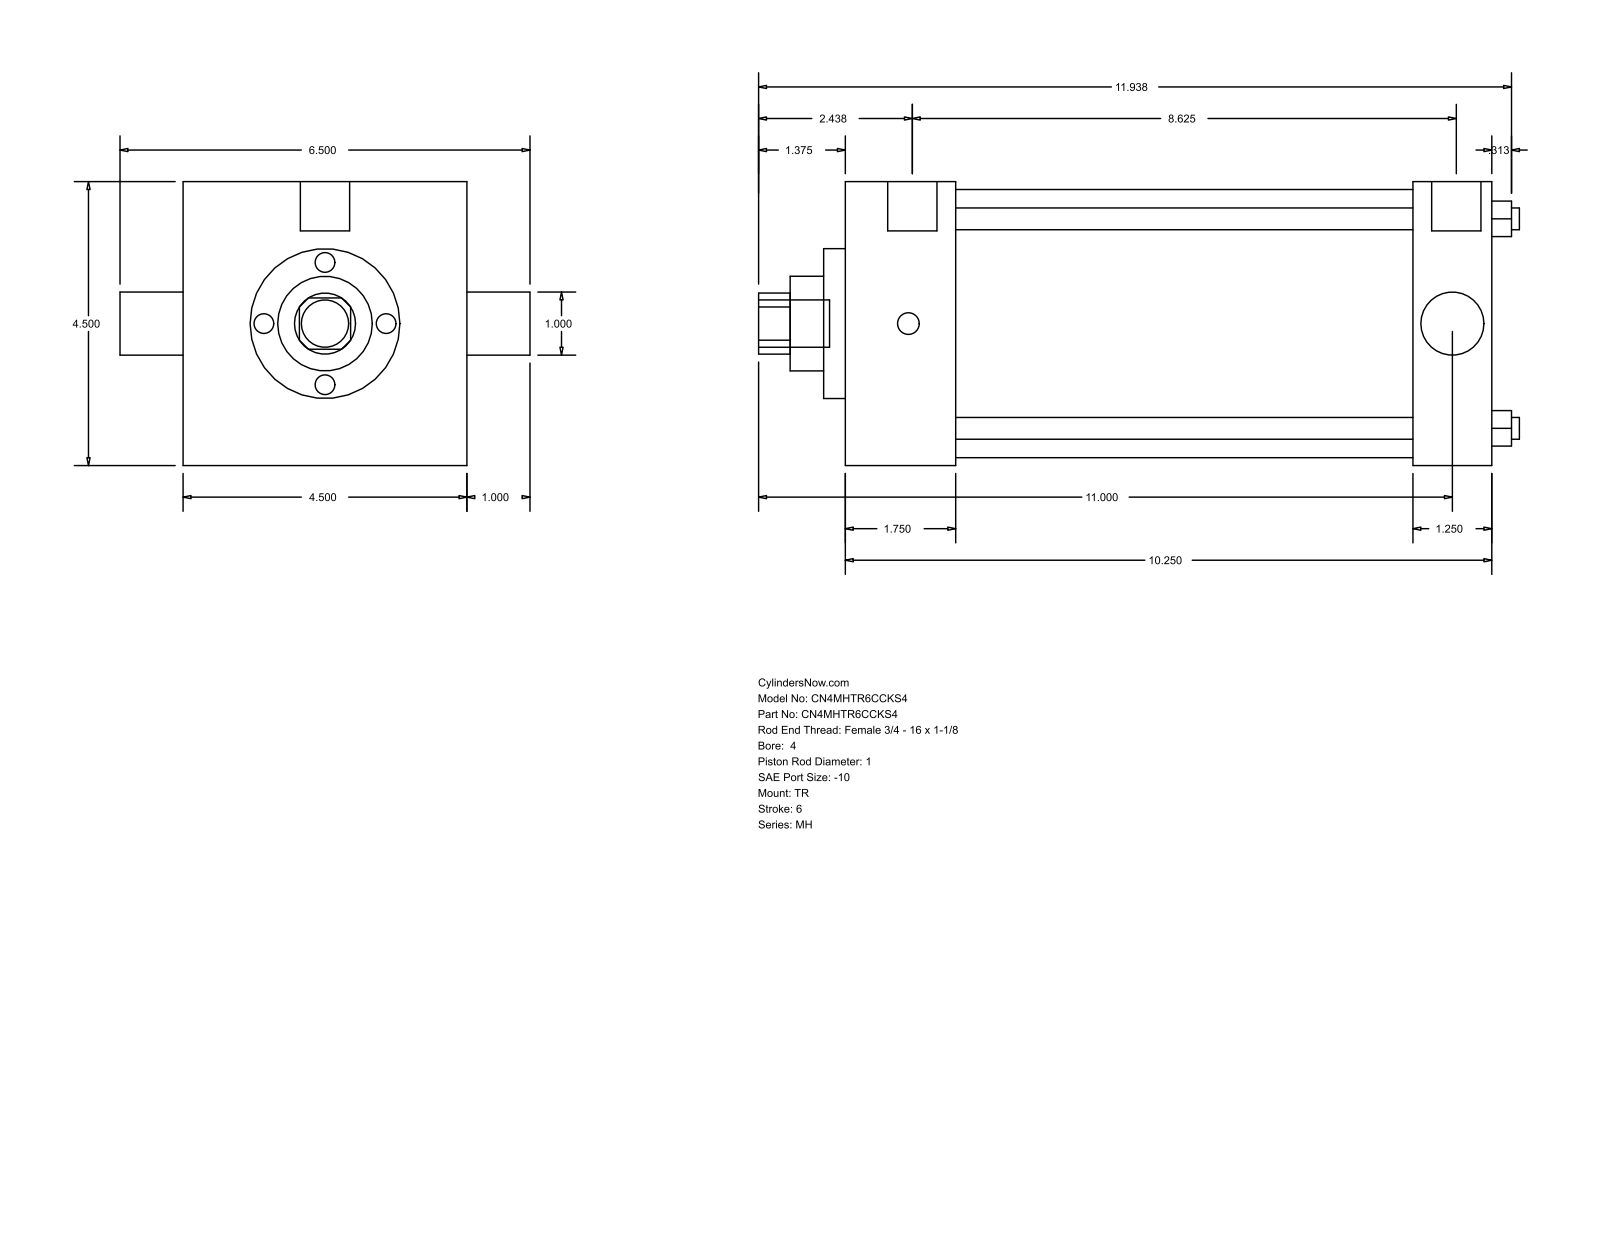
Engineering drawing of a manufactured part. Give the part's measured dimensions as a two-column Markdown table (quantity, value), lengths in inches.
| quantity | value |
| --- | --- |
| part name | MH_TR__0400_1 |
| STEP written by | GSSL Pune (CONFIG_CONTROL_DESIGN) |
| units | inches |
| bodies | 0 solids, 86 faces (61 planar, 25 cylindrical, 0 other) |
| overall size | 12.063 × 6.5 × 4.5 |
| round holes (diameter × count) | 0.345 × 4, 1 × 2, 1.5 × 1, 2.375 × 1, 4.25 × 1 |
| round bosses / shafts (diameter × count) | 0.344 × 3, 0.781 × 2, 0.75 × 1 |
| partial cylindrical surfaces (radius × count) | 0.484 × 1 |
| main face-to-face distances | 4.5, 10.25, 1.75, 8.5, 9, 7.25, 1.25, 0.344, 2.094, 9.344 |
| hole center spacings | 2.347, 3.32, 4.695 |
